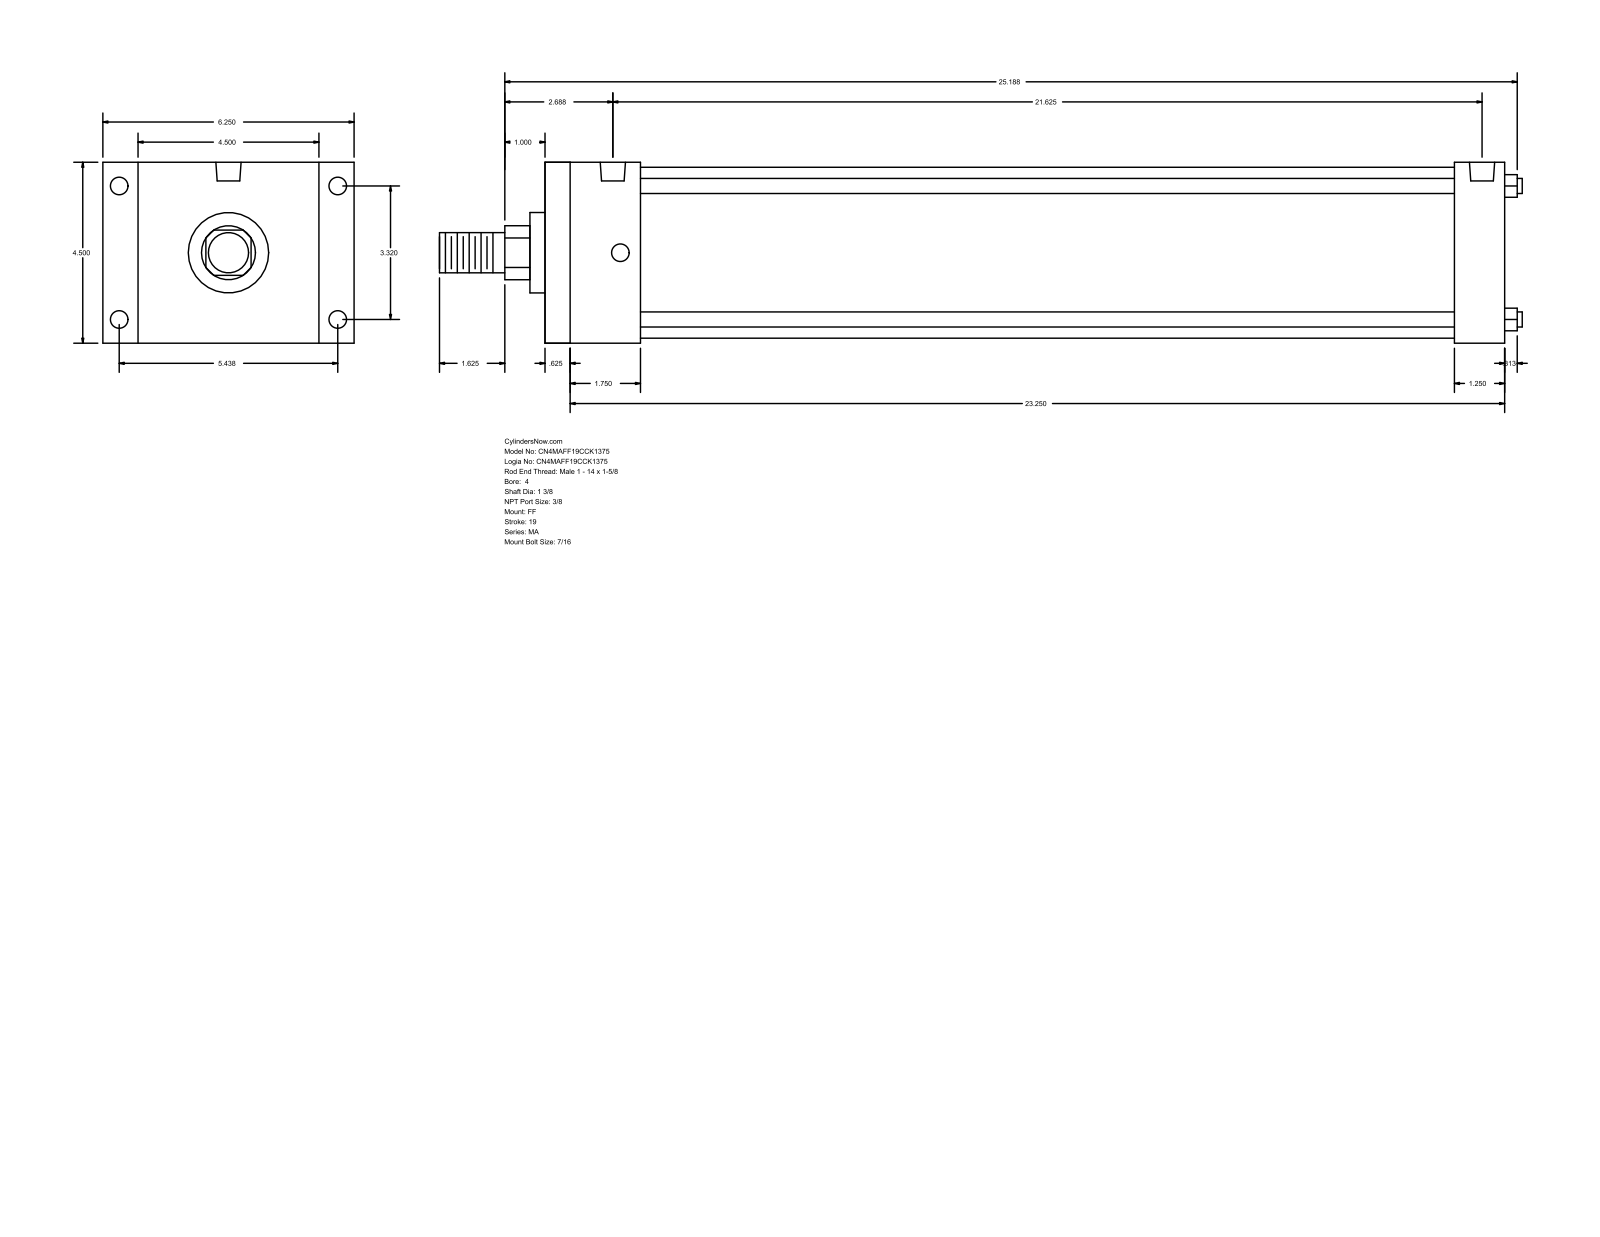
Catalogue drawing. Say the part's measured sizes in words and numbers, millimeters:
The part is named "MA_FF__0400_1.375". Its 3-D file was written by "GSSL Pune (CONFIG_CONTROL_DESIGN)". It is 0 solids with 92 faces: 64 planar, 28 cylindrical and 0 other. Overall it measures 684.21 by 158.75 by 114.3 millimeters. Round holes: 8 of diameter 11.11, 2 of diameter 15.93. Round bosses or shafts: 4 of diameter 9.53, 1 of diameter 107.95, 1 of diameter 50.8, 1 of diameter 34.92, 1 of diameter 25.4. Partial cylindrical surfaces (rounded edges, fillets, slot ends): 1 of radius 17.06. The main face-to-face distances are 114.3, 606.43, 15.87, 590.56, 22.23, 136.53, 574.68, 558.81, 31.75, 60.32. The hole center spacings are 4.77, 84.32, 138.12, 161.82, 539.74, 544.51, 549.28.
